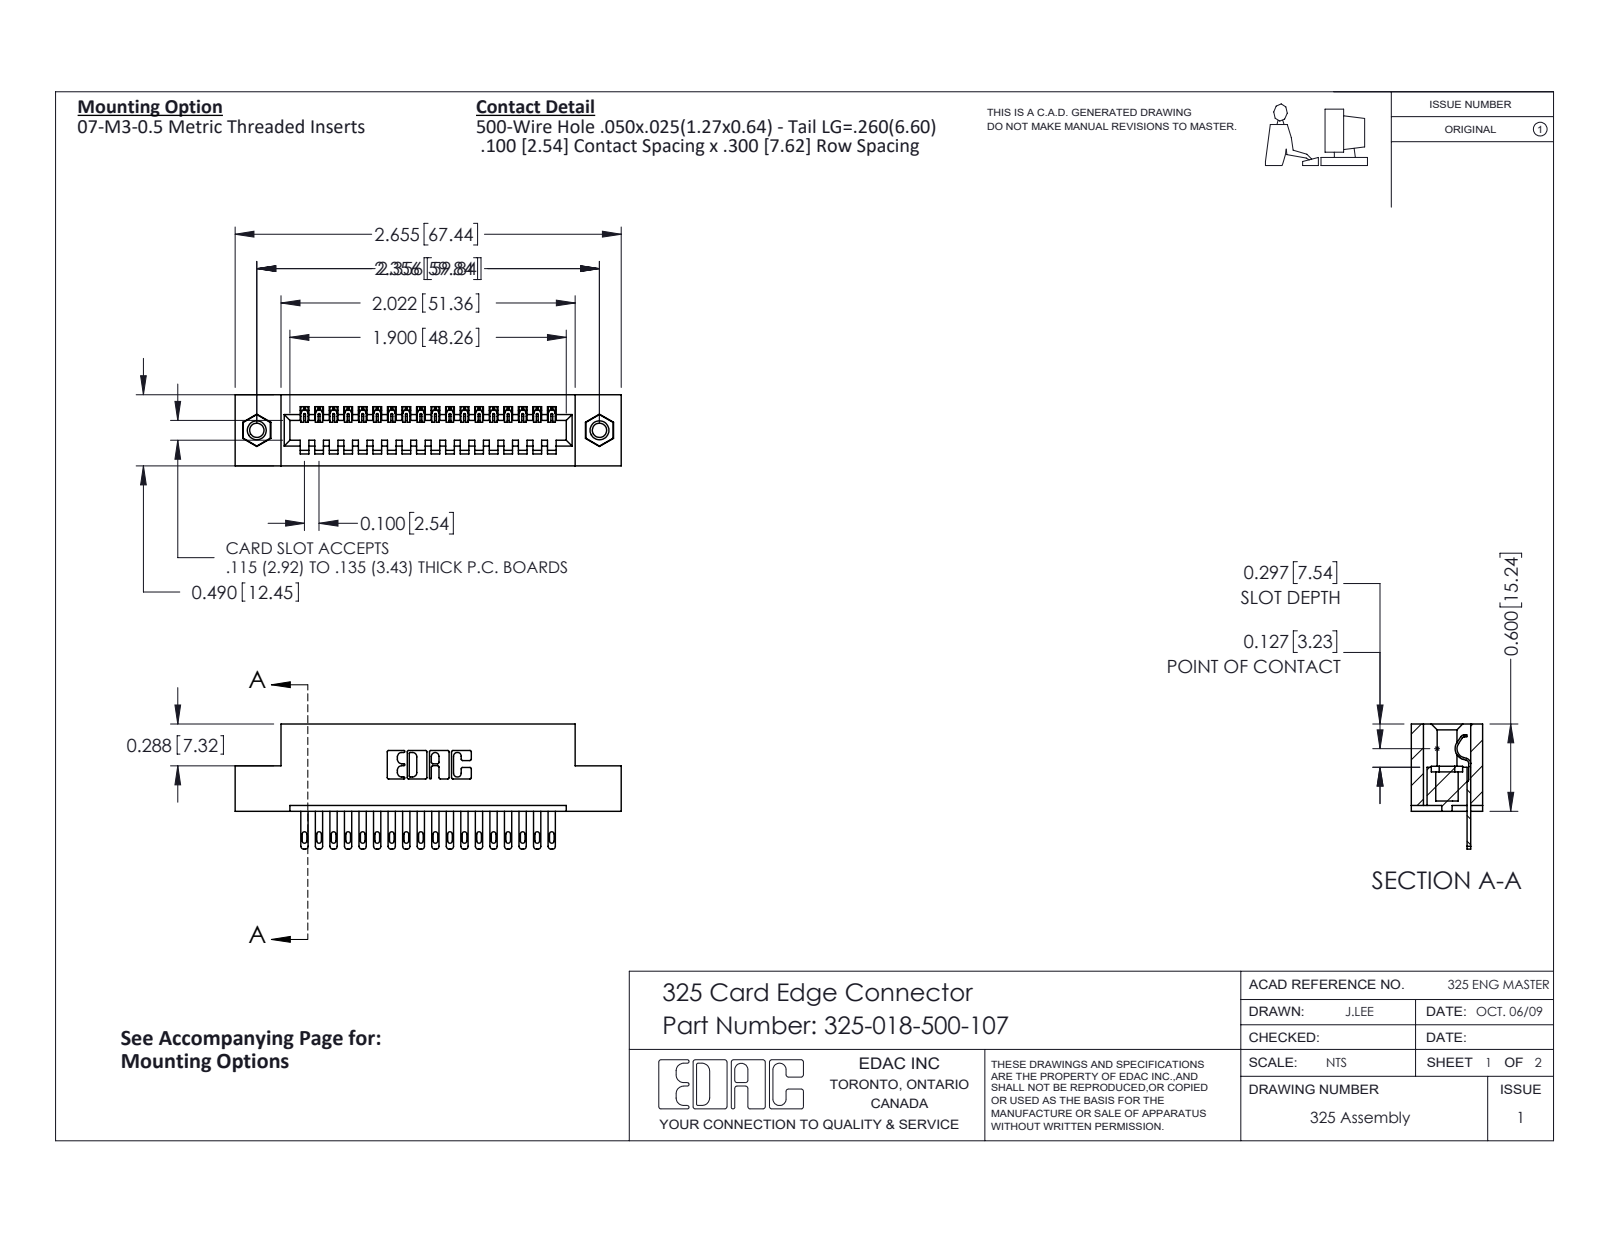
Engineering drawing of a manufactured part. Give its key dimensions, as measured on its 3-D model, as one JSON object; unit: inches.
{"part_name": "325 Part_TI; 325-018-500-107; 325-292-001_325-293-100; 345-250-001_345-250-005-103", "step_written_by": "SolidWorks 2016 (CONFIG_CONTROL_DESIGN)", "units": "inches", "bodies": {"solids": 21, "faces": 1146, "planar": 750, "cylindrical": 380, "other": 16}, "overall_size": [2.655, 0.86, 0.49], "volume_in3": 0.511, "surface_area_in2": 13.65, "round_holes": [[0.098, 2], [0.125, 2], [0.16, 2]], "round_bosses_or_shafts": [[0.155, 2]], "partial_cylinders_radius": [[0.006, 36], [0.016, 36], [0.02, 36], [0.01, 22], [0.007, 6], [0.031, 6], [0.026, 3], [0.014, 1]], "face_to_face_distances": [0.083, 0.407, 0.3, 0.49, 0.107, 0.383, 0.025, 0.6, 0.2, 0.04], "hole_center_spacings": [2.356]}
